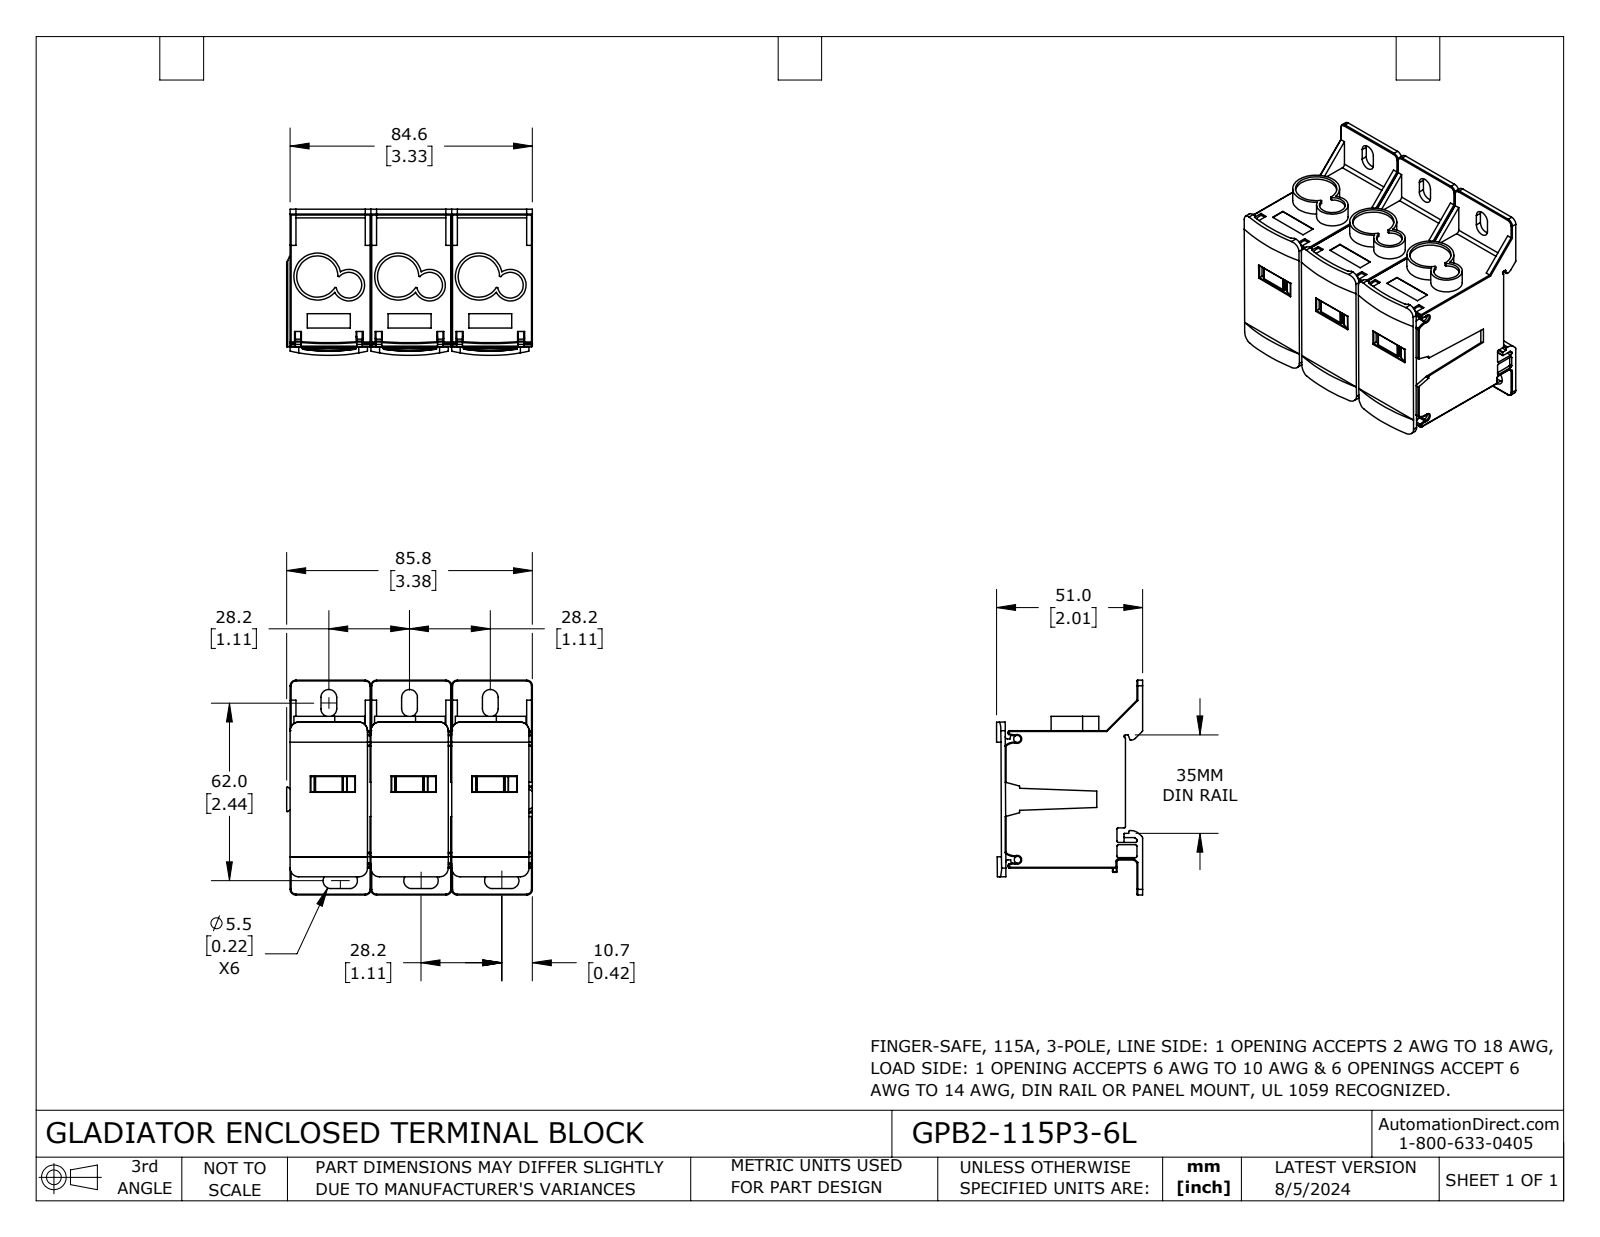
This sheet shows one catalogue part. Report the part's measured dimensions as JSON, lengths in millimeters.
{"part_name": "GPB2-115P3-6L", "step_written_by": "SolidWorks 2023 (CONFIG_CONTROL_DESIGN)", "units": "millimeters", "bodies": {"solids": 1, "faces": 1252, "planar": 421, "cylindrical": 618, "other": 213}, "overall_size": [85.8, 75, 51], "volume_mm3": 185000, "surface_area_mm2": 35120, "round_holes": [[9, 3], [14.4, 3], [2.5, 1]], "round_bosses_or_shafts": [[16.4, 3], [2.5, 1]], "partial_cylinders_radius": [[0.2, 151], [0.3, 77], [0.5, 24], [2, 13], [5, 13], [2.7, 12], [3, 12], [61.5, 12]], "face_to_face_distances": [4, 2, 6, 1, 84.6, 48, 47, 7, 52, 28.2], "hole_center_spacings": [28.2, 11.4, 17.4, 39.3, 56.4, 45.5, 67.5]}
